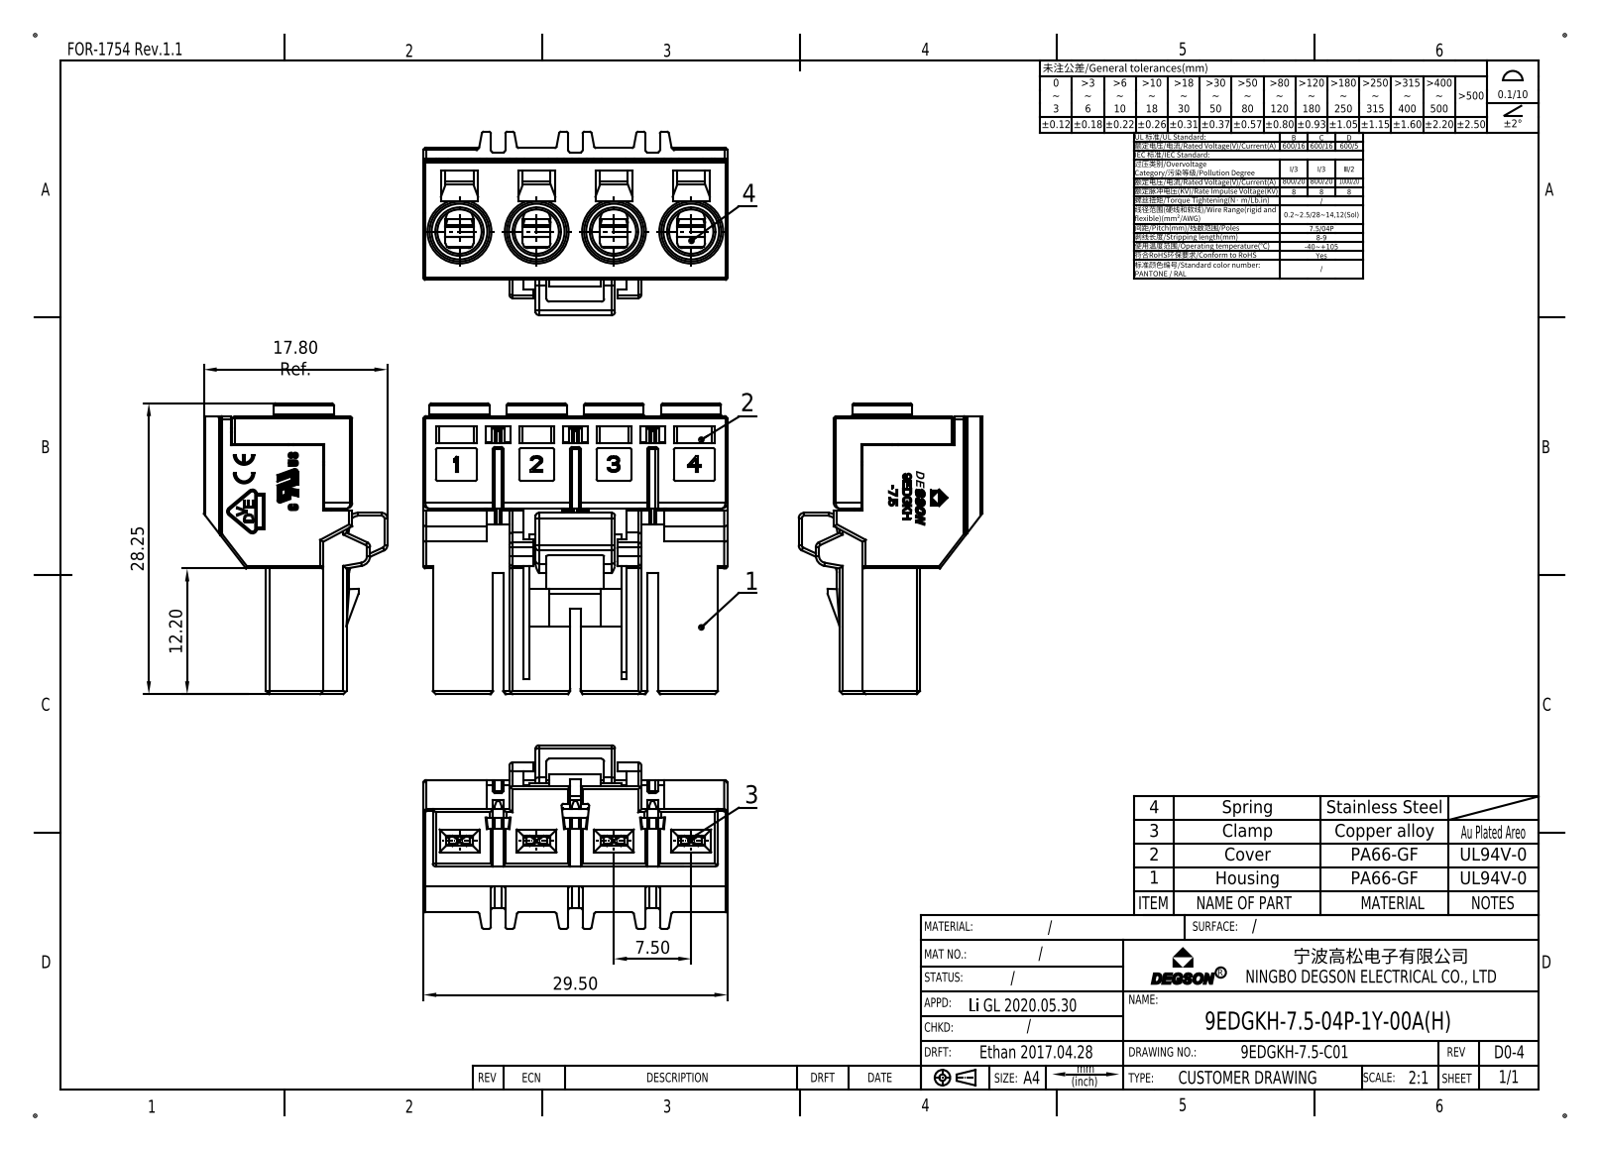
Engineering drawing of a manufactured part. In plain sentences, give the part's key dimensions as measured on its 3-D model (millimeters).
The part is named "9EDGKH-7.5-04P 20200608". Its 3-D file was written by "SIEMENS PLM Software NX 8.5 (CONFIG_CONTROL_DESIGN)". It is 1 solid with 678 faces: 495 planar, 115 cylindrical and 68 other. Overall it measures 29.5 by 28.25 by 17.81 millimeters. Its volume is 7 371 cubic millimeters and its surface area 4 754 square millimeters. Round holes: 4 of diameter 4.3. Round bosses or shafts: 4 of diameter 5.8. Partial cylindrical surfaces (rounded edges, fillets, slot ends): 46 of radius 0.2, 27 of radius 0.3, 4 of radius 0.6, 3 of radius 0.5, 3 of radius 1. The main face-to-face distances are 2.8, 8.36, 5.56, 0.8, 0.9, 4.45, 10.01, 12.81, 9.23, 4.78. The hole center spacings are 7.5, 15, 22.5.
